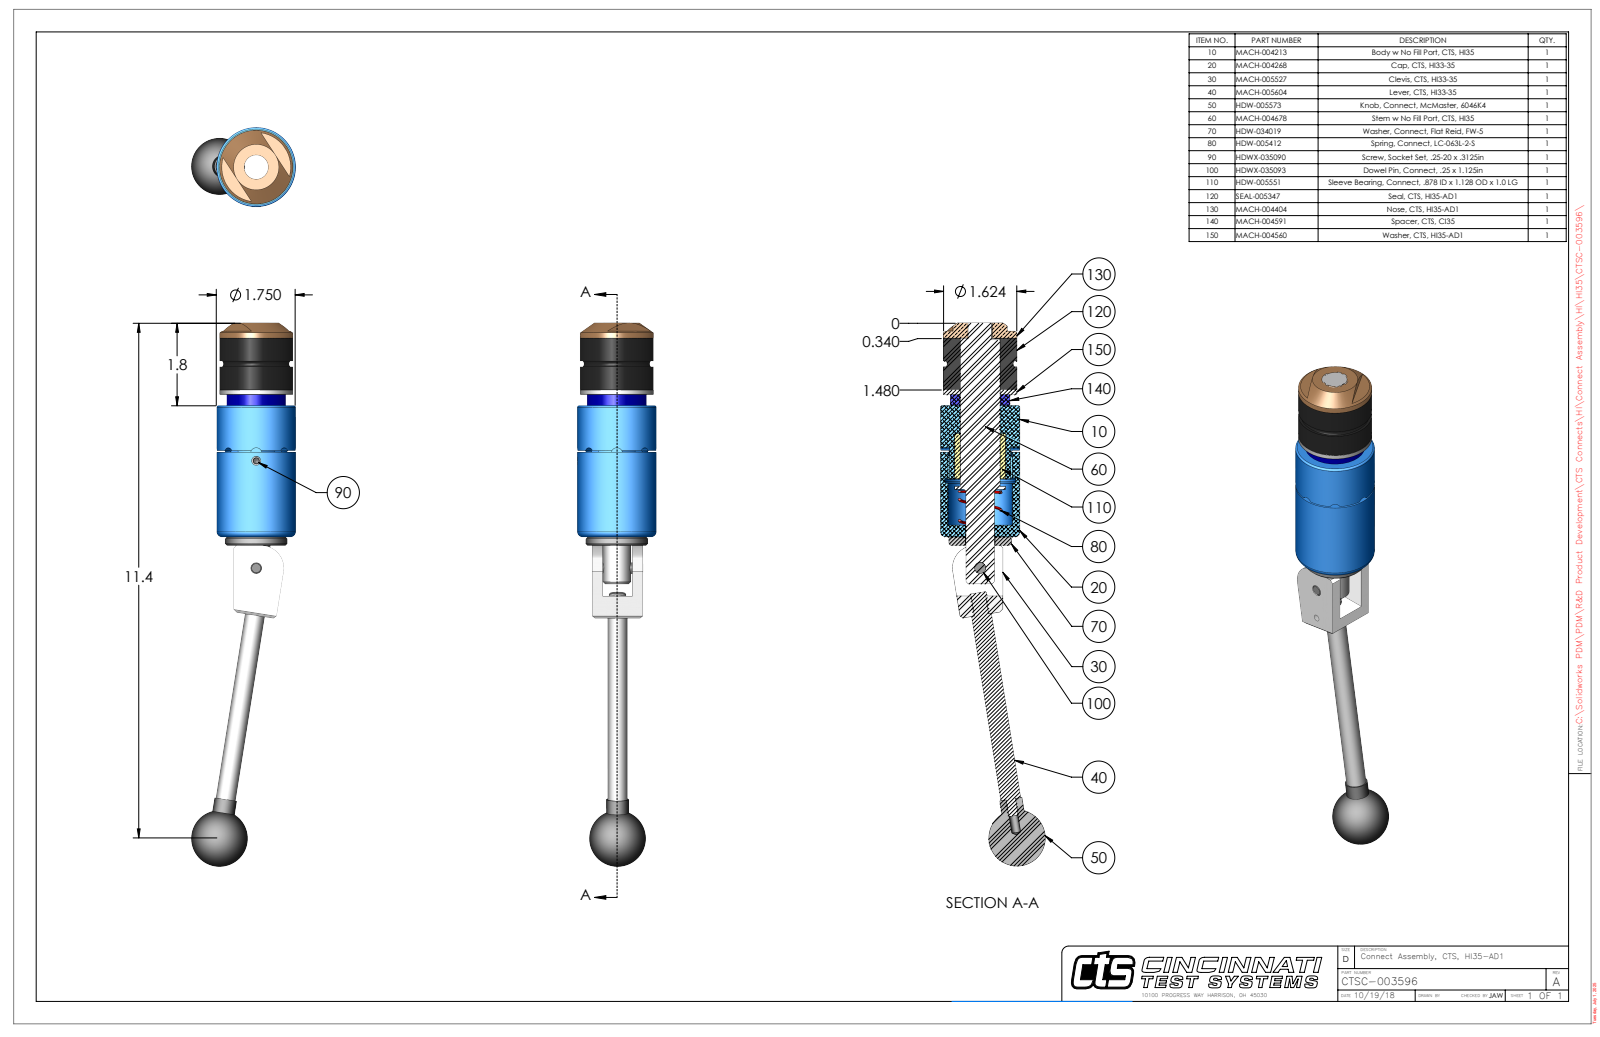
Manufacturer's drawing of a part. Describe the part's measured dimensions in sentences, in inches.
The part is named "CTSC-003596". Its 3-D file was written by "SolidWorks 2023 (AUTOMOTIVE_DESIGN)". It is 11 solids with 262 faces: 96 planar, 104 cylindrical and 62 other. Overall it measures 12.039 by 2.312 by 1.75 inches. Its volume is 13.59 cubic inches and its surface area 83.29 square inches. Round holes: 2 of diameter 0.201, 1 of diameter 0.15, 1 of diameter 0.249, 1 of diameter 0.251, 1 of diameter 0.313, 1 of diameter 0.531, 1 of diameter 0.635, 1 of diameter 0.656, 1 of diameter 0.875, 1 of diameter 0.876, 1 of diameter 0.885, 1 of diameter 1.419. Round bosses or shafts: 2 of diameter 0.25, 1 of diameter 1.75, 1 of diameter 1.624, 1 of diameter 1.38, 1 of diameter 1.312, 1 of diameter 0.871, 1 of diameter 0.869, 1 of diameter 0.625. Partial cylindrical surfaces (rounded edges, fillets, slot ends): 4 of radius 0.125, 2 of radius 0.029, 1 of radius 0.5, 1 of radius 0.695, 1 of radius 0.824. The main face-to-face distances are 1.14, 4.402, 3.262, 1.49, 0.35, 2.912, 1.25, 0.11, 0.24, 3.152. The hole center spacings are 0.74, 2.376, 3.116.
